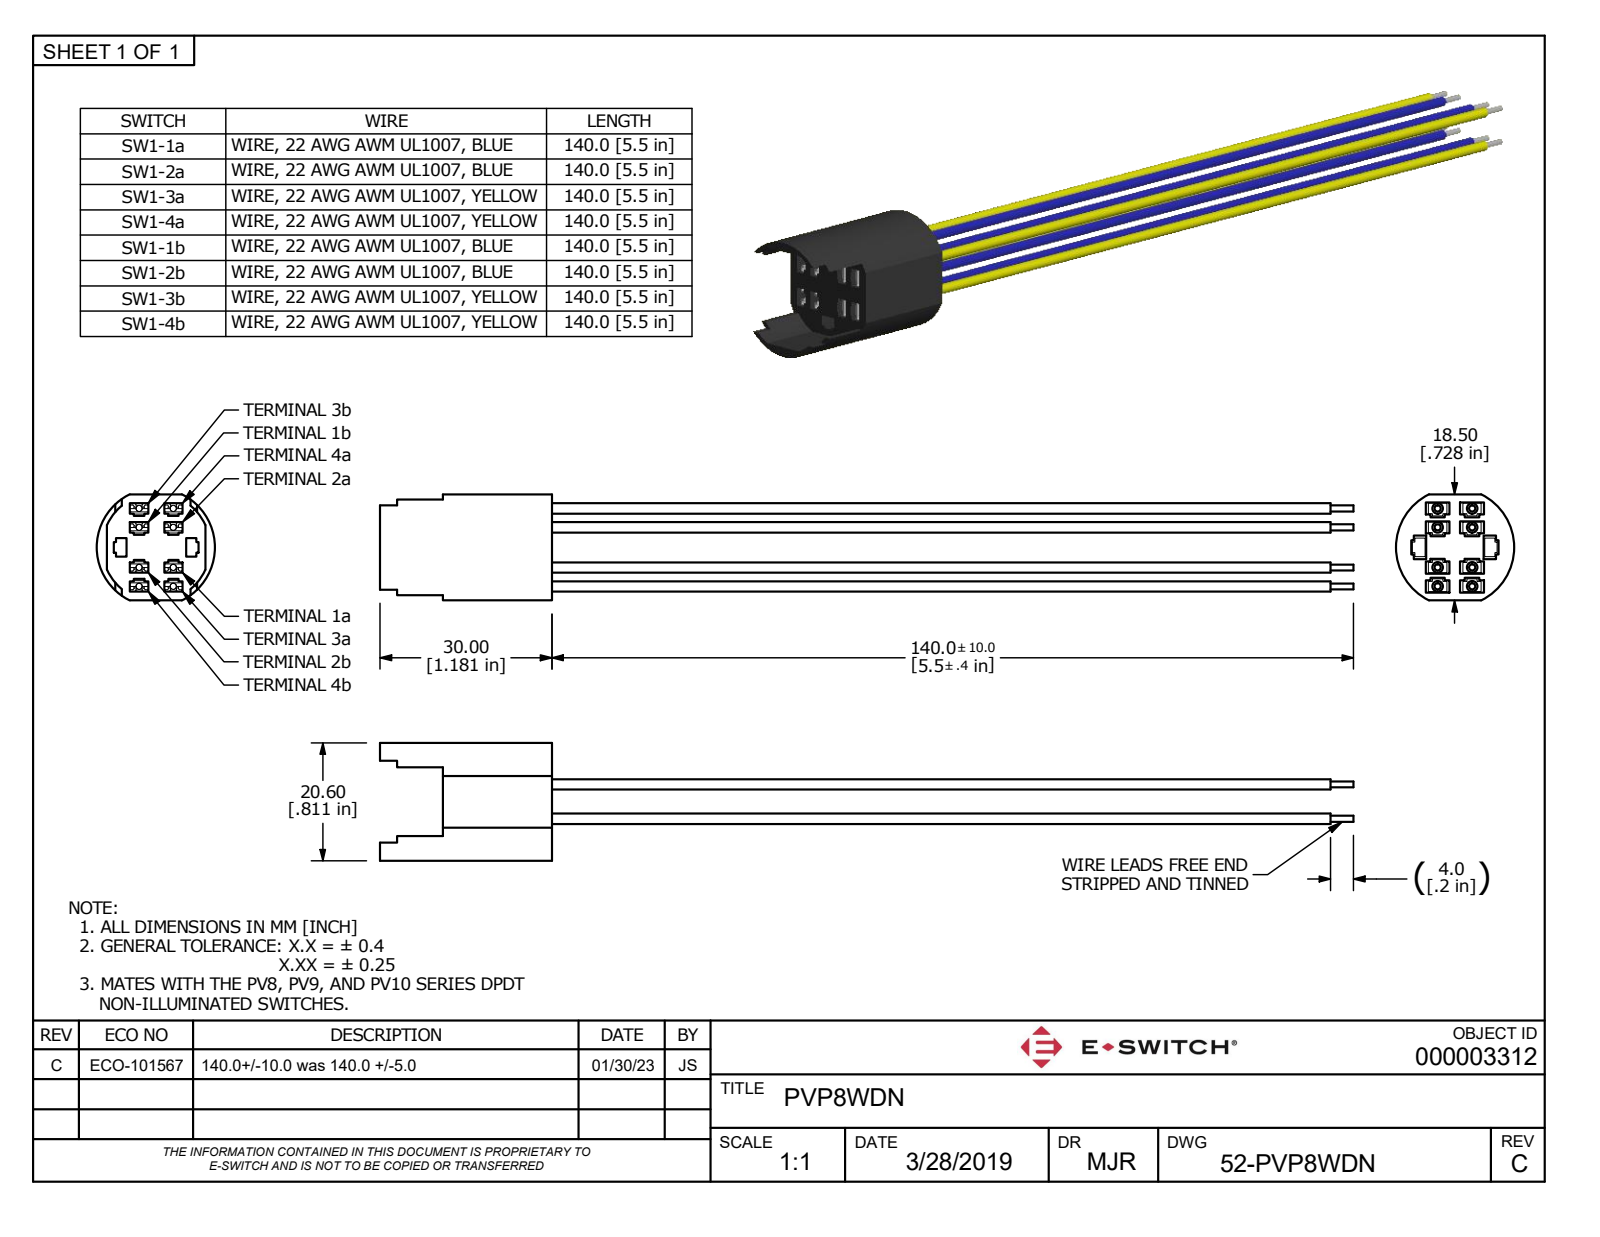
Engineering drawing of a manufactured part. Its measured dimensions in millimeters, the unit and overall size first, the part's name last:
Units: millimetres
Overall size (bounding box): 170 × 20.6 × 18.5
Round bosses / shafts (diameter × count): ⌀1.8 ×8
Partial cylindrical surfaces — rounded edges, fillets, slot ends (radius × count): R0.25 ×48, R0.5 ×16, R0.52 ×8, R9.45 ×1, R10.3 ×1
Main face-to-face distances: 3.3, 6, 19, 2.2, 2.37, 13.2, 12.27, 2.6, 3.67, 2.8
Volume: 8 167 mm³ · Surface area: 11 972 mm²
Bodies: 1 solid, 540 faces (398 planar, 94 cylindrical, 48 other)
Part name (STEP PRODUCT): PVP8WDN
STEP written by: Autodesk Inventor 2018 (AP242_MANAGED_MODEL_BASED_3D_ENGINEERING_MIM_LF)
